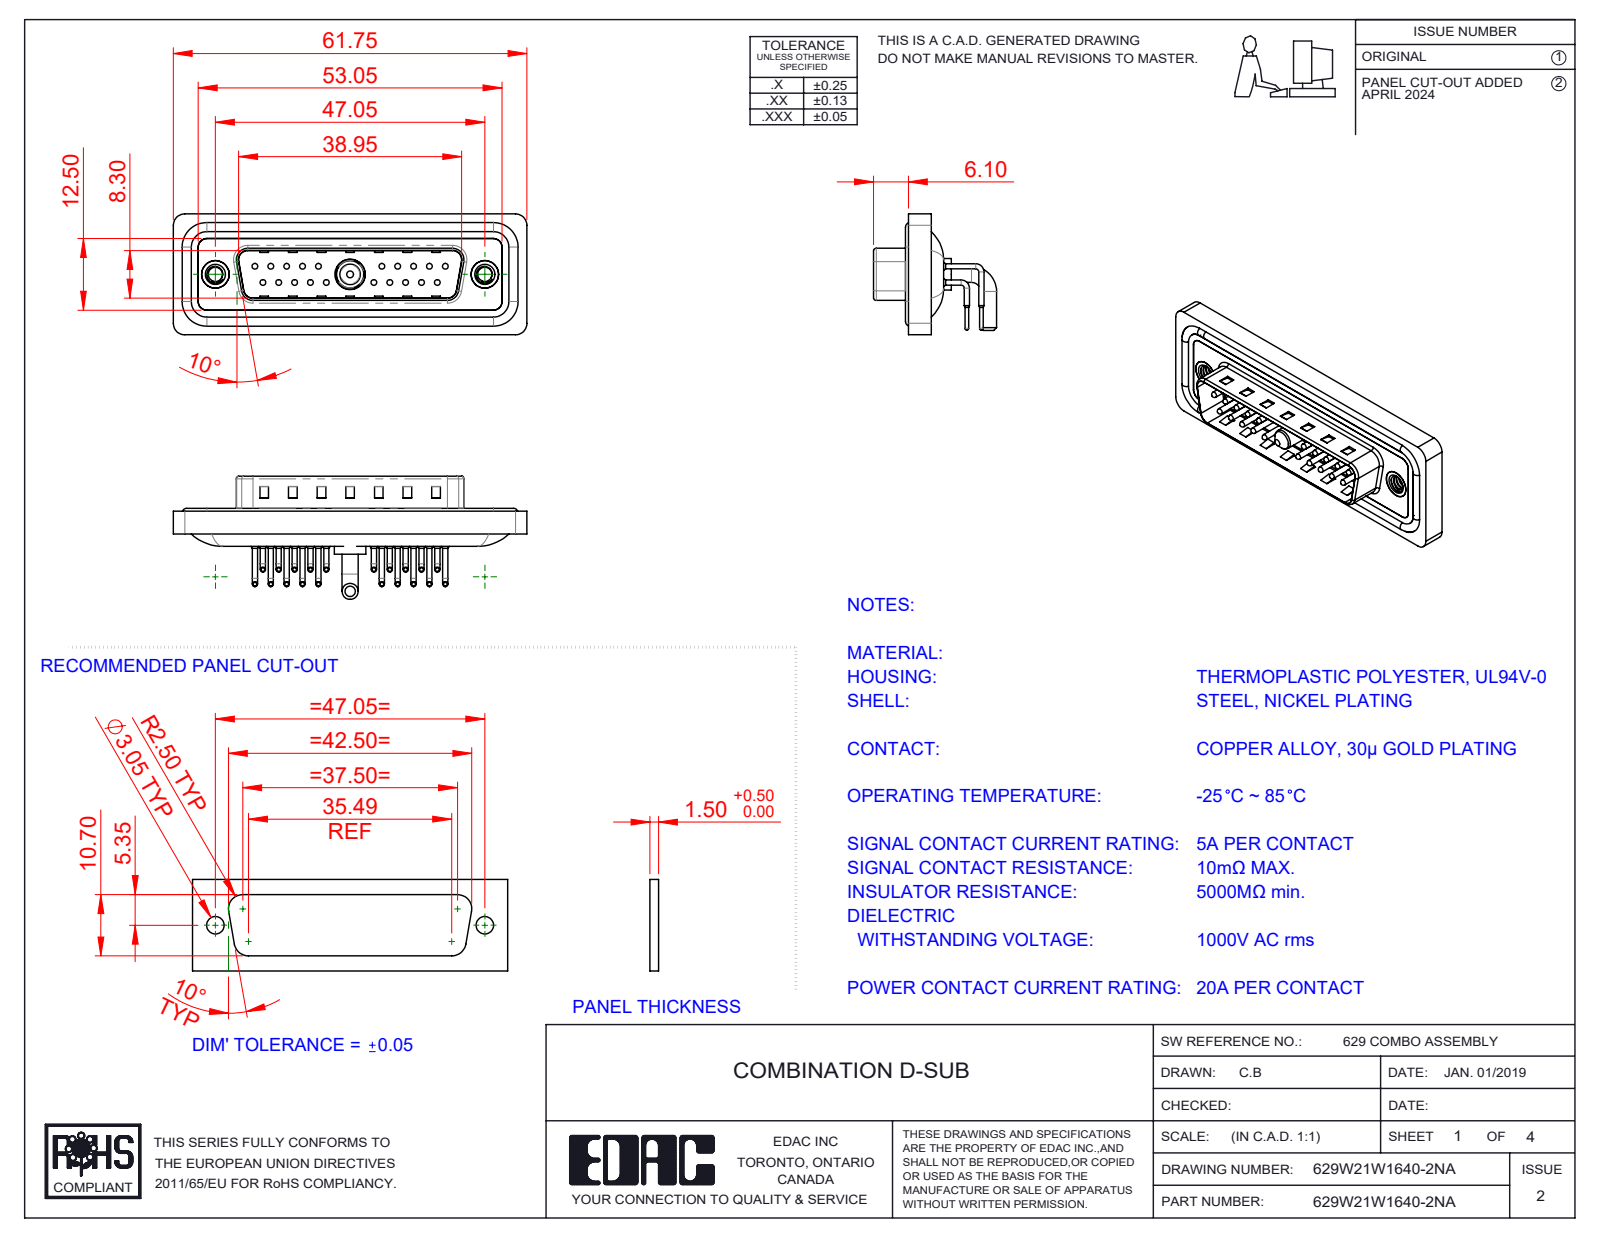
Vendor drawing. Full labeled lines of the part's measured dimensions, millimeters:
Part name (STEP PRODUCT): 629Combo Shell Front_25 Contacts; 629Combo Shell Rear_25 Contacts; 629Combo Housing_21W1; Power Pin_20A RA (+5 more)
STEP written by: SolidWorks 2023 (CONFIG_CONTROL_DESIGN)
Units: millimetres
Bodies: 29 solids, 2720 faces (1499 planar, 927 cylindrical, 294 other)
Overall size (bounding box): 61.75 × 21.5 × 21.1
Volume: 7 421 mm³ · Surface area: 12 724 mm²
Round holes (diameter × count): ⌀0.75 ×20, ⌀1.6 ×20, ⌀2 ×20, ⌀2.5 ×2, ⌀4 ×2, ⌀4.8 ×2, ⌀5 ×2, ⌀4.85 ×1, ⌀5.3 ×1
Round bosses / shafts (diameter × count): ⌀0.9 ×40, ⌀1.5 ×20, ⌀1 ×20, ⌀0.65 ×20, ⌀1.6 ×4, ⌀4.9 ×2, ⌀2.8 ×2, ⌀5.5 ×1
Partial cylindrical surfaces — rounded edges, fillets, slot ends (radius × count): R1.01 ×20, R1.5 ×18, R2 ×18, R0.5 ×8, R1.6 ×8, R0.25 ×4, R0.6 ×4, R0.65 ×4
Main face-to-face distances: 0.4, 2.9, 0.8, 4.1, 1.1, 2.1, 1.6, 4.5, 1.5, 2.5
Hole centre spacings: 3.16, 2.77, 5.54, 8.31, 5.04, 19.39, 20.97, 22.16
